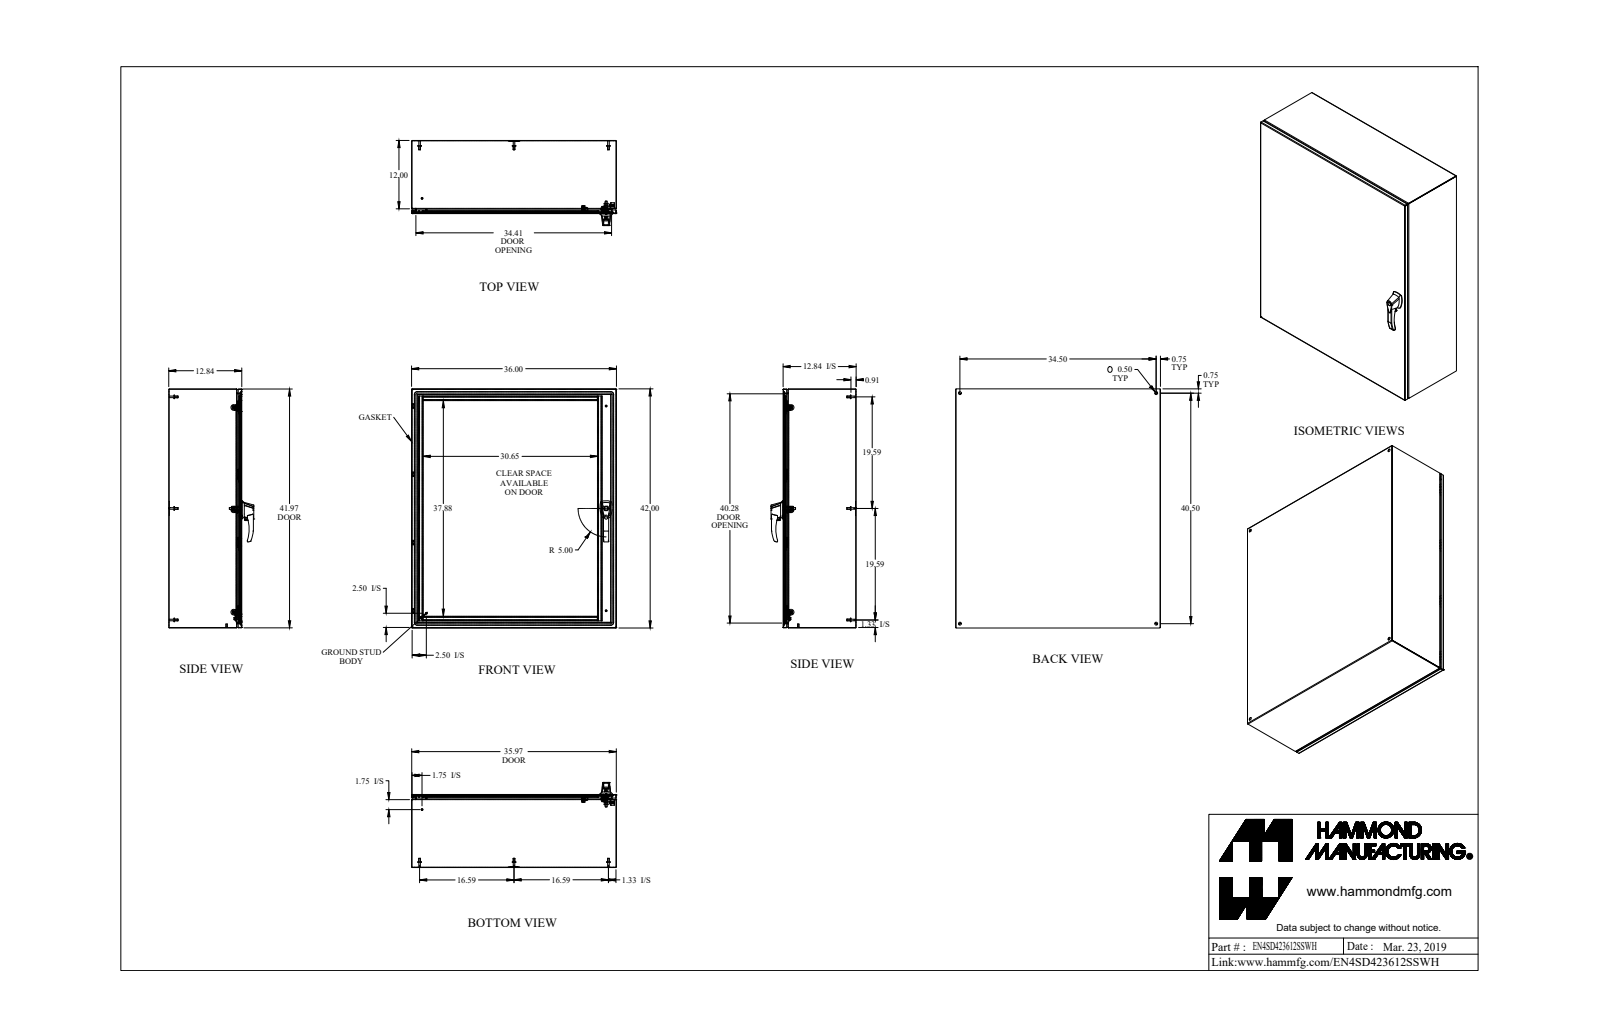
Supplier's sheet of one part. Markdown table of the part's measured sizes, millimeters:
| quantity | value |
| --- | --- |
| part name | EN4SD423612SSWH |
| STEP written by | SolidWorks 2018 (AUTOMOTIVE_DESIGN) |
| units | millimeters |
| bodies | 68 solids, 1786 faces (779 planar, 668 cylindrical, 339 other) |
| overall size | 1066.8 × 914.4 × 379.9 |
| volume | 6 843 000 mm³ |
| surface area | 7 405 000 mm² |
| round holes (diameter × count) | 4.5 × 6, 12.7 × 4, 5 × 3, 6.4 × 3, 6.7 × 3, 8 × 3, 10.5 × 3, 6.5 × 2, 9.5 × 2, 10 × 2, 4.4 × 1, 5.9 × 1 |
| round bosses / shafts (diameter × count) | 8 × 10, 7 × 8, 15.9 × 7, 6.4 × 7, 9.5 × 6, 4 × 6, 25.4 × 3, 13 × 3 |
| partial cylindrical surfaces (radius × count) | 1.2 × 32, 0.3 × 24, 0.9 × 18, 2.7 × 18, 1.6 × 14, 2.4 × 10, 0.4 × 9, 3.2 × 9 |
| main face-to-face distances | 1.8, 324.4, 322.6, 326.2, 912.6, 1065, 910.7, 914.4, 1063.1, 1066.8 |
| hole center spacings | 20, 913.6, 456.8, 456.8, 457.2, 515.1, 851.3, 876.3 |
